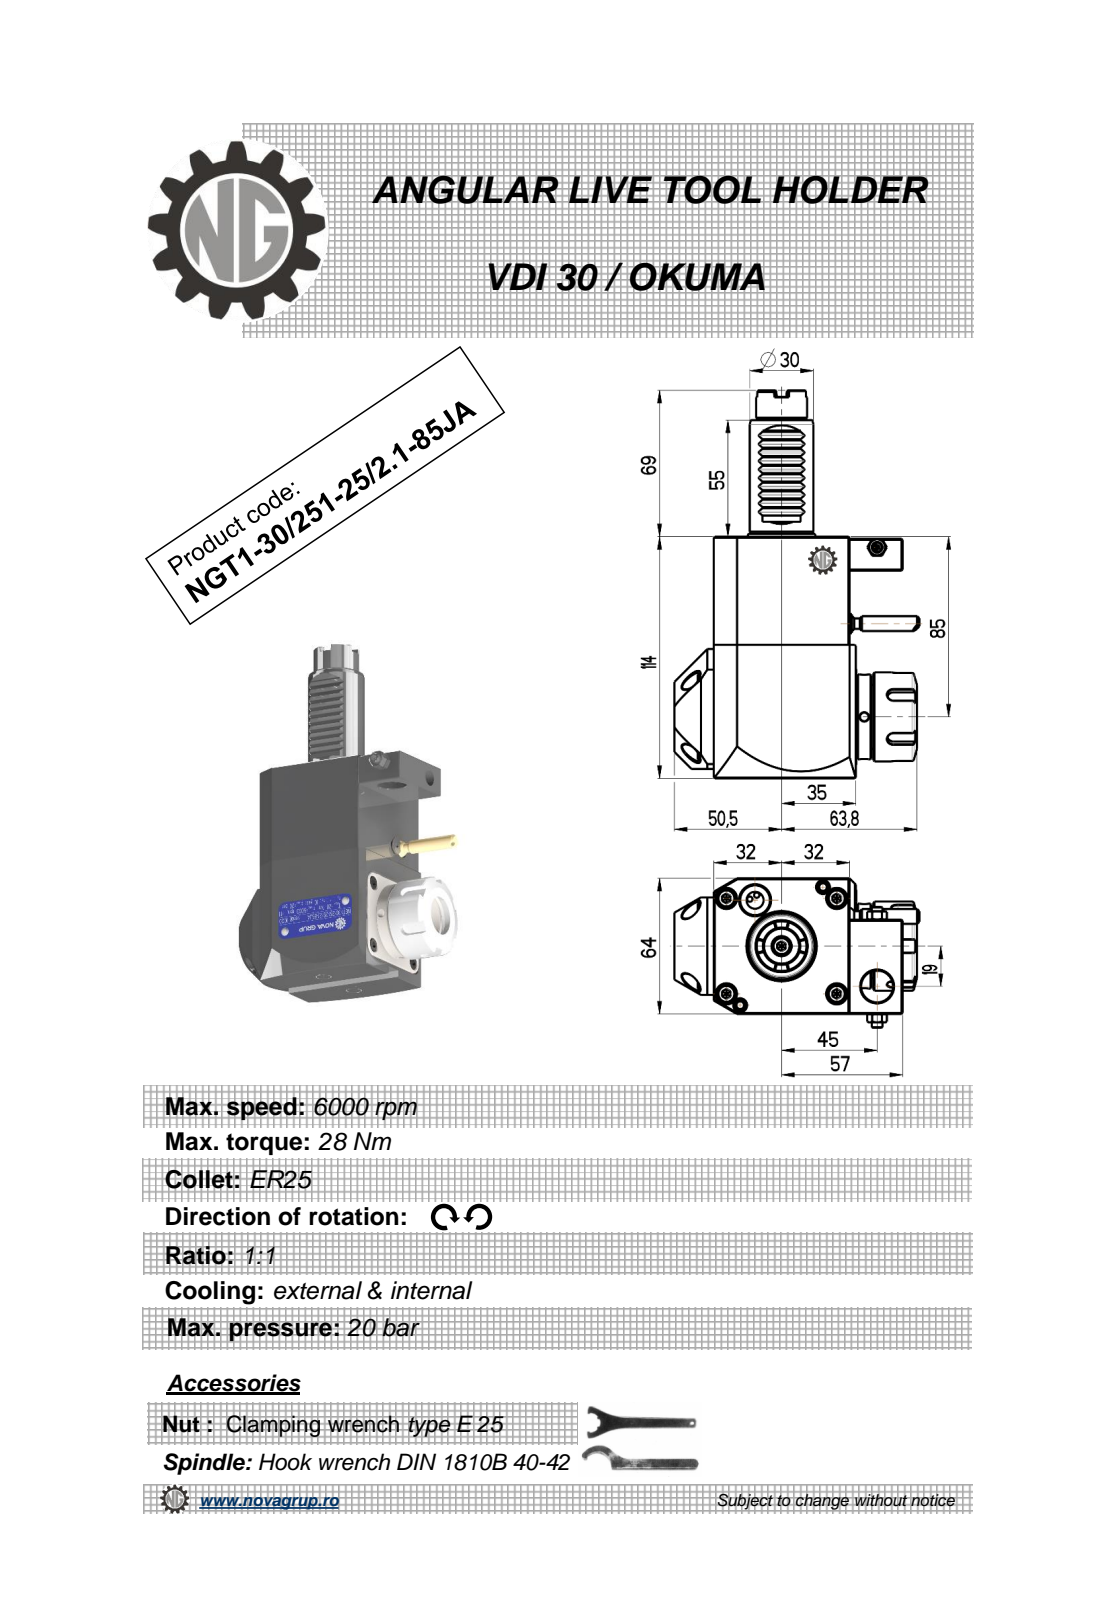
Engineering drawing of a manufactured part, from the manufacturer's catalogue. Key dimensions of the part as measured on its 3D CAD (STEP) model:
Part name (STEP PRODUCT): NGT1_30_251_25_2_1_85JA
STEP written by: PRO/ENGINEER BY PARAMETRIC TECHNOLOGY CORPORATION, 2010280 (CONFIG_CONTROL_DESIGN)
Units: millimetres
Bodies: 1 solid, 497 faces (216 planar, 99 cylindrical, 182 other)
Overall size (bounding box): 183 × 115.38 × 70.5
Volume: 590 848 mm³ · Surface area: 58 062 mm²
Round holes (diameter × count): ⌀4 ×3, ⌀2.5 ×1, ⌀3 ×1, ⌀3.8 ×1, ⌀4.2 ×1, ⌀6 ×1, ⌀9 ×1, ⌀15 ×1, ⌀17 ×1, ⌀20.3 ×1
Round bosses / shafts (diameter × count): ⌀5 ×2, ⌀42 ×1, ⌀40 ×1, ⌀33 ×1, ⌀30 ×1, ⌀24 ×1, ⌀9 ×1, ⌀8.5 ×1
Partial cylindrical surfaces — rounded edges, fillets, slot ends (radius × count): R0.26 ×12, R0.3 ×10, R0.17 ×6, R3 ×5, R160 ×2, R32 ×1
Main face-to-face distances: 64, 114, 67.2, 3.2, 67, 3, 1, 113, 16, 15
Hole centre spacings: 9, 19.94, 32.88, 35.39, 38.95, 46.17, 48.85, 76.5
